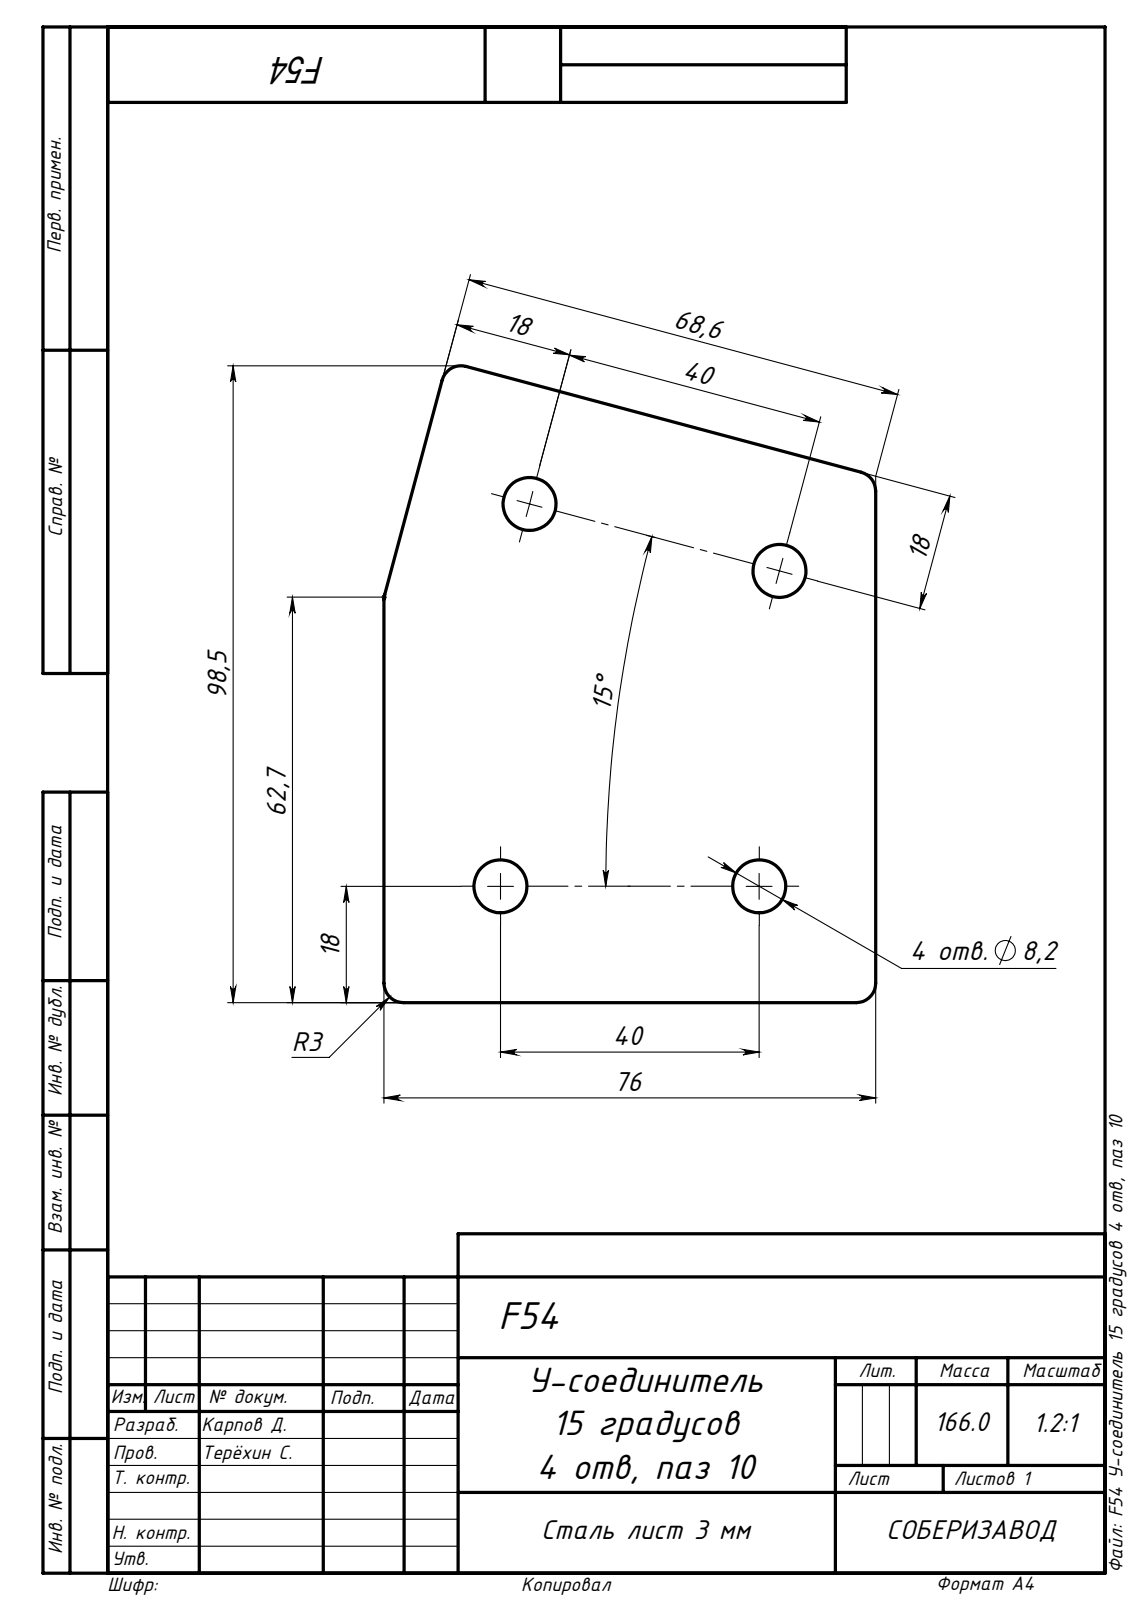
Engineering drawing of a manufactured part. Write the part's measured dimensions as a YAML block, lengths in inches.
part_name: "F54 У-соединитель 15 градусов 4 отв, паз 10"
step_written_by: "SolidWorks 2020 (AUTOMOTIVE_DESIGN)"
units: inches
bodies: {solids: 1, faces: 20, planar: 7, cylindrical: 13, other: 0}
overall_size: [3.878, 2.992, 0.118]
volume: 1.2
surface_area: 22.3
round_holes:
  - {diameter: 0.323, count: 4}
partial_cylinders:
  - {radius: 0.118, count: 5}
face_to_face_distances: [0.118, 2.992]
hole_center_spacings: [1.575, 1.925, 2.335, 2.564, 2.716]
